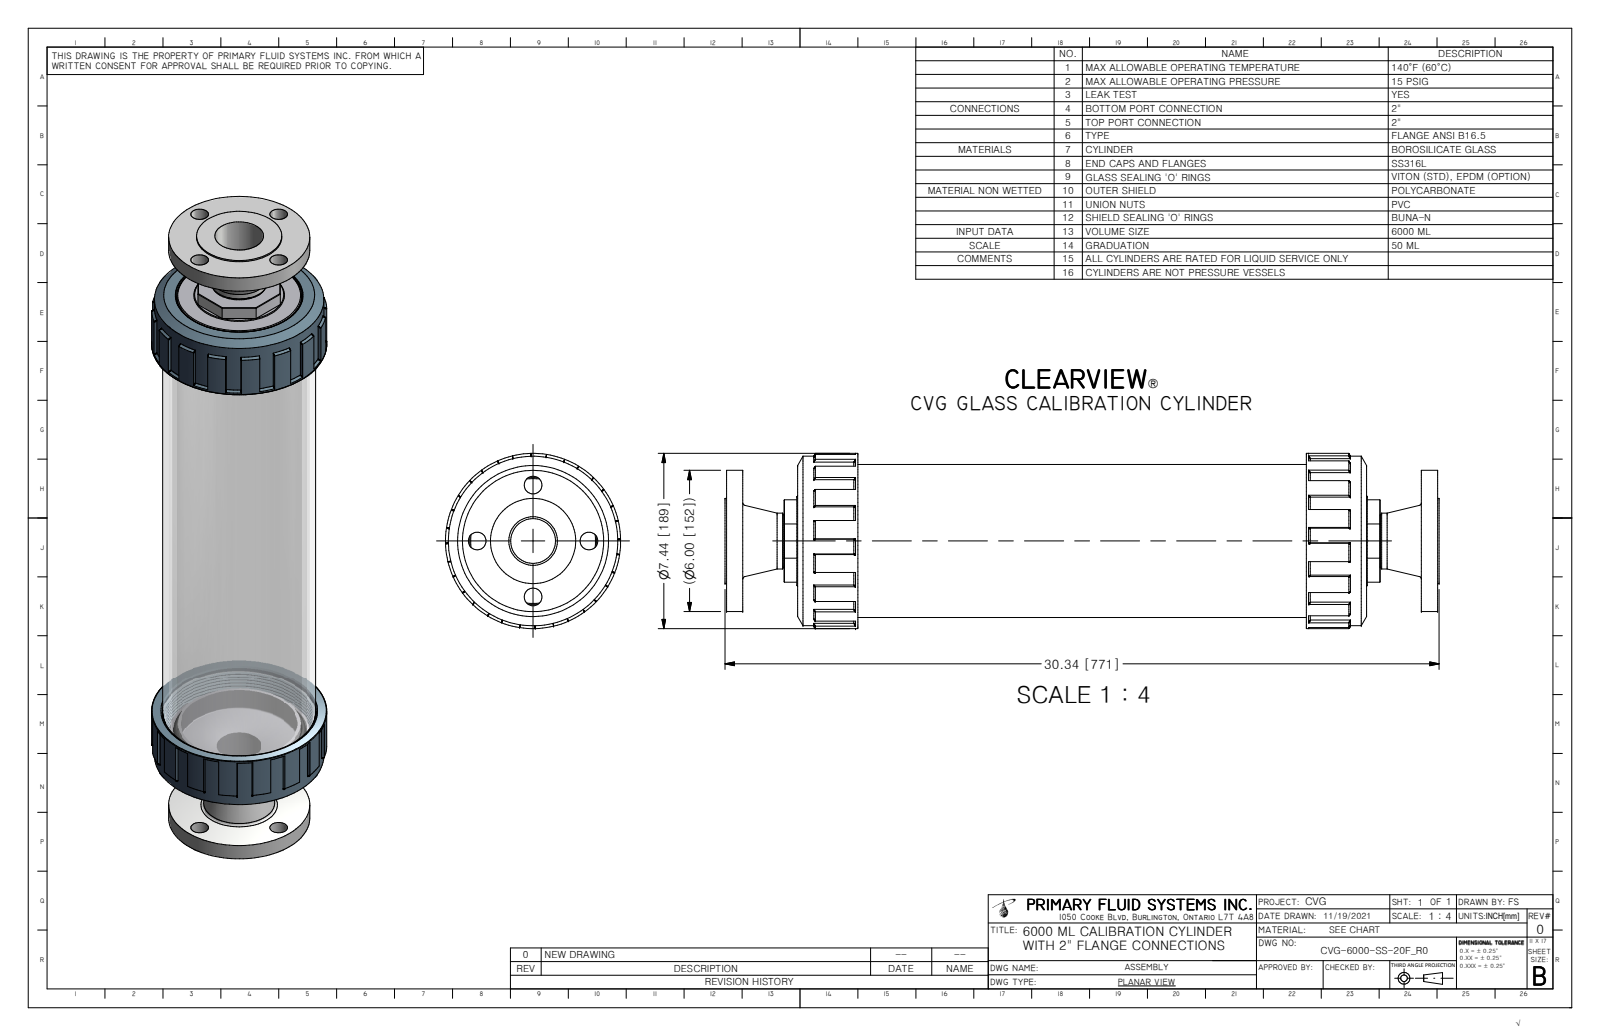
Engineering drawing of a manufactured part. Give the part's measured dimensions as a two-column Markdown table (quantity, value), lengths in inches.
| quantity | value |
| --- | --- |
| STEP written by | Autodesk Inventor 2009 (AUTOMOTIVE_DESIGN) |
| units | inches |
| bodies | 3 solids, 385 faces (140 planar, 97 cylindrical, 148 other) |
| overall size | 30.337 × 7.445 × 7.445 |
| volume | 97.83 in³ |
| surface area | 2 475 in² |
| round holes (diameter × count) | 0.75 × 4, 1.9 × 1, 2.067 × 1, 2.219 × 1, 4.98 × 1, 5.315 × 1, 5.386 × 1, 5.709 × 1, 5.76 × 1, 5.97 × 1, 6.535 × 1 |
| round bosses / shafts (diameter × count) | 7.445 × 1, 7.201 × 1, 6.5 × 1, 6.496 × 1, 6.26 × 1, 6.25 × 1, 6 × 1, 5.3 × 1 |
| partial cylindrical surfaces (radius × count) | 0.335 × 2, 3.38 × 2 |
| main face-to-face distances | 2.327, 26.505, 0.69, 3.017, 27.195, 29.522, 24.178, 28.832, 5.576, 24.636 |
| hole center spacings | 2.375, 3.359, 4.75 |
